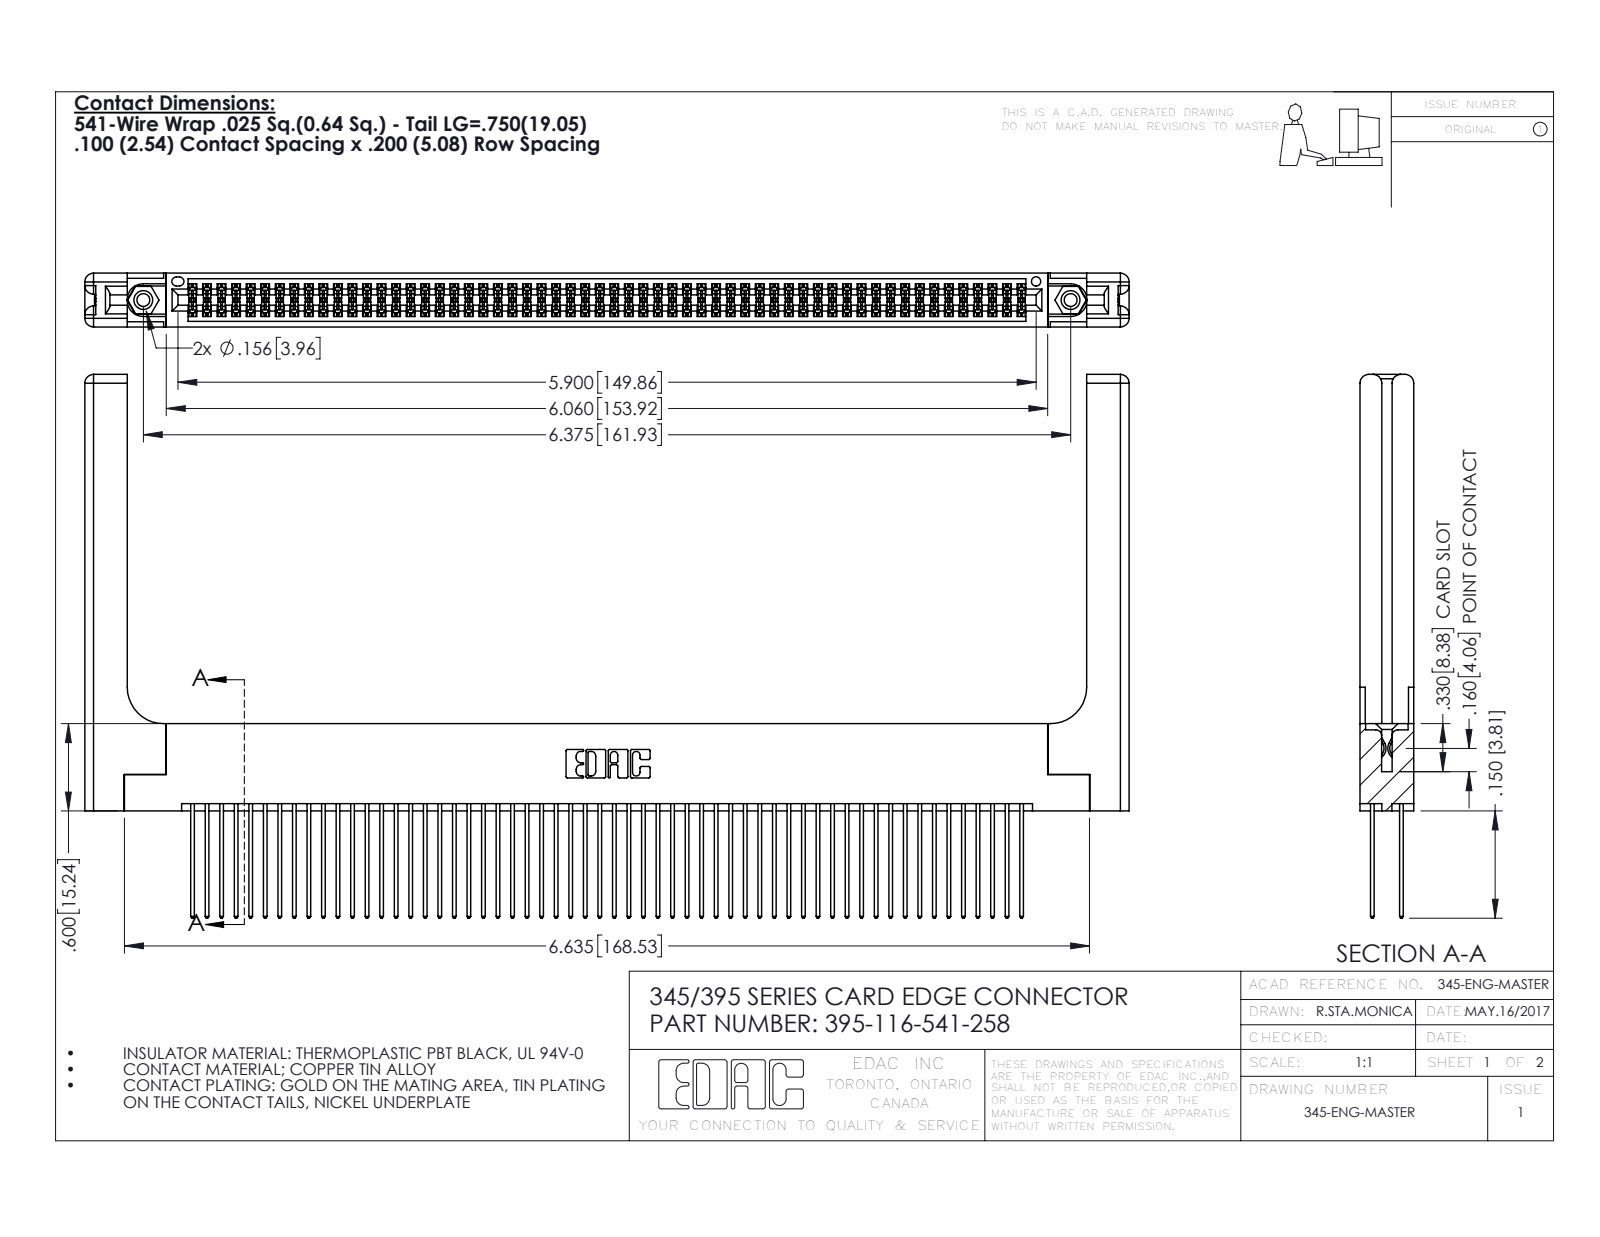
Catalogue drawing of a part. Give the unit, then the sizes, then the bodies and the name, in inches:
Units: inches
Overall size (bounding box): 7.179 × 3.737 × 0.37
Round holes (diameter × count): ⌀0.089 ×2, ⌀0.125 ×2, ⌀0.156 ×2, ⌀0.064 ×1
Round bosses / shafts (diameter × count): ⌀0.155 ×2
Partial cylindrical surfaces — rounded edges, fillets, slot ends (radius × count): R0.006 ×174, R0.01 ×116, R0.01 ×22, R0.06 ×16, R0.007 ×6, R0.031 ×6, R0.026 ×3, R0.014 ×2
Main face-to-face distances: 0.072, 0.298, 0.2, 0.098, 0.272, 0.025, 0.37, 0.225, 0.175, 0.148
Hole centre spacings: 0.27, 6.139, 6.375
Volume: 1.648 in³ · Surface area: 55.62 in²
Bodies: 121 solids, 6182 faces (4056 planar, 2066 cylindrical, 60 other)
Part name (STEP PRODUCT): 345 Part_Flush Mounting Lugs - 0.156 Dia-TH; 345-250-001_345-250-001-102; 395-116-541-258; 345-292-001_345-293-141 (+1 more)
STEP written by: SolidWorks 2016 (CONFIG_CONTROL_DESIGN)
